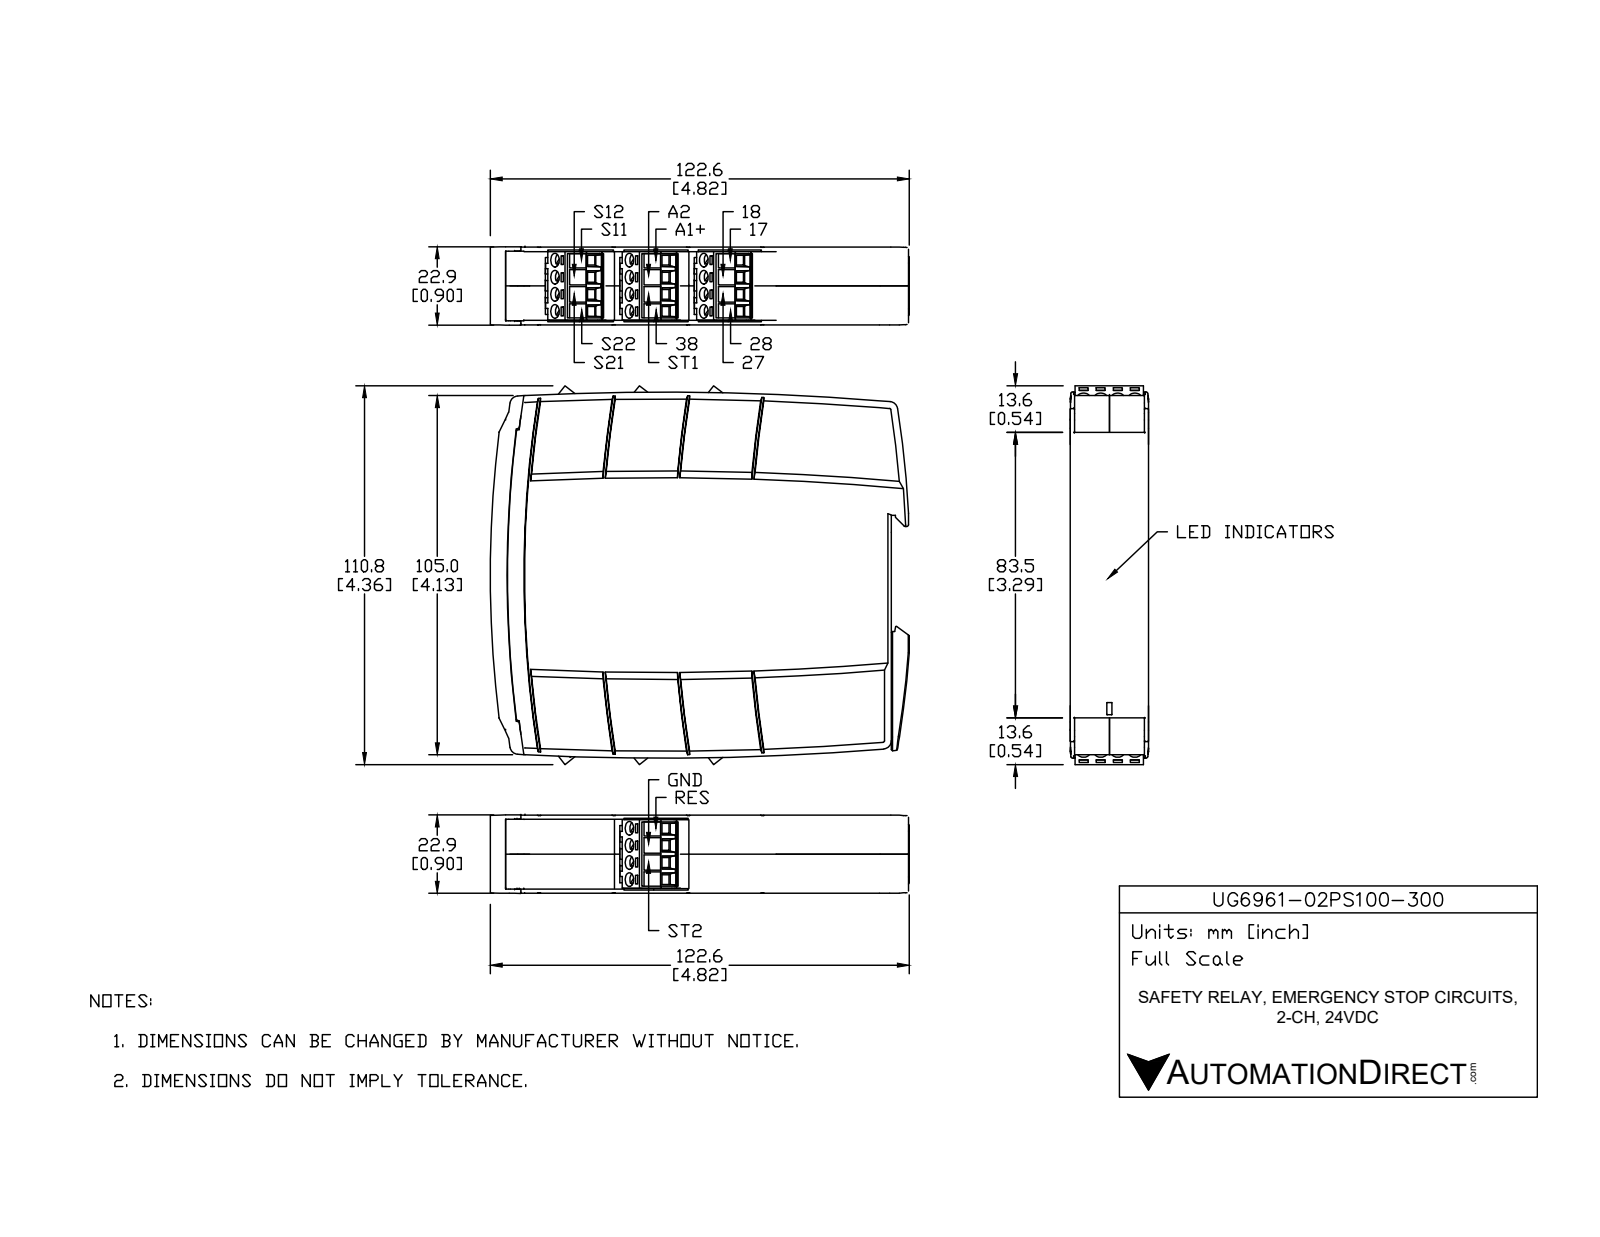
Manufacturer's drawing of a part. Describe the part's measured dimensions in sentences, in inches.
The part is named "UG6961-02PS100-300". Its 3-D file was written by "SolidWorks 2021 (AUTOMOTIVE_DESIGN)". It is 1 solid with 403 faces: 356 planar, 38 cylindrical and 9 other. Overall it measures 4.813 by 4.355 by 0.886 inches. Its volume is 16.69 cubic inches and its surface area 58.39 square inches. Round holes: 16 of diameter 0.157. Partial cylindrical surfaces (rounded edges, fillets, slot ends): 9 of radius 0.012, 7 of radius 0.094, 2 of radius 0.02, 2 of radius 31.496. The main face-to-face distances are 0.886, 0.049, 0.837, 0.675, 0.528, 0.787, 0.567, 1.35, 1.056, 1.242. The hole center spacings are 0.197, 0.394, 0.563, 0.563, 1.074, 0.528, 0.528, 0.591.
